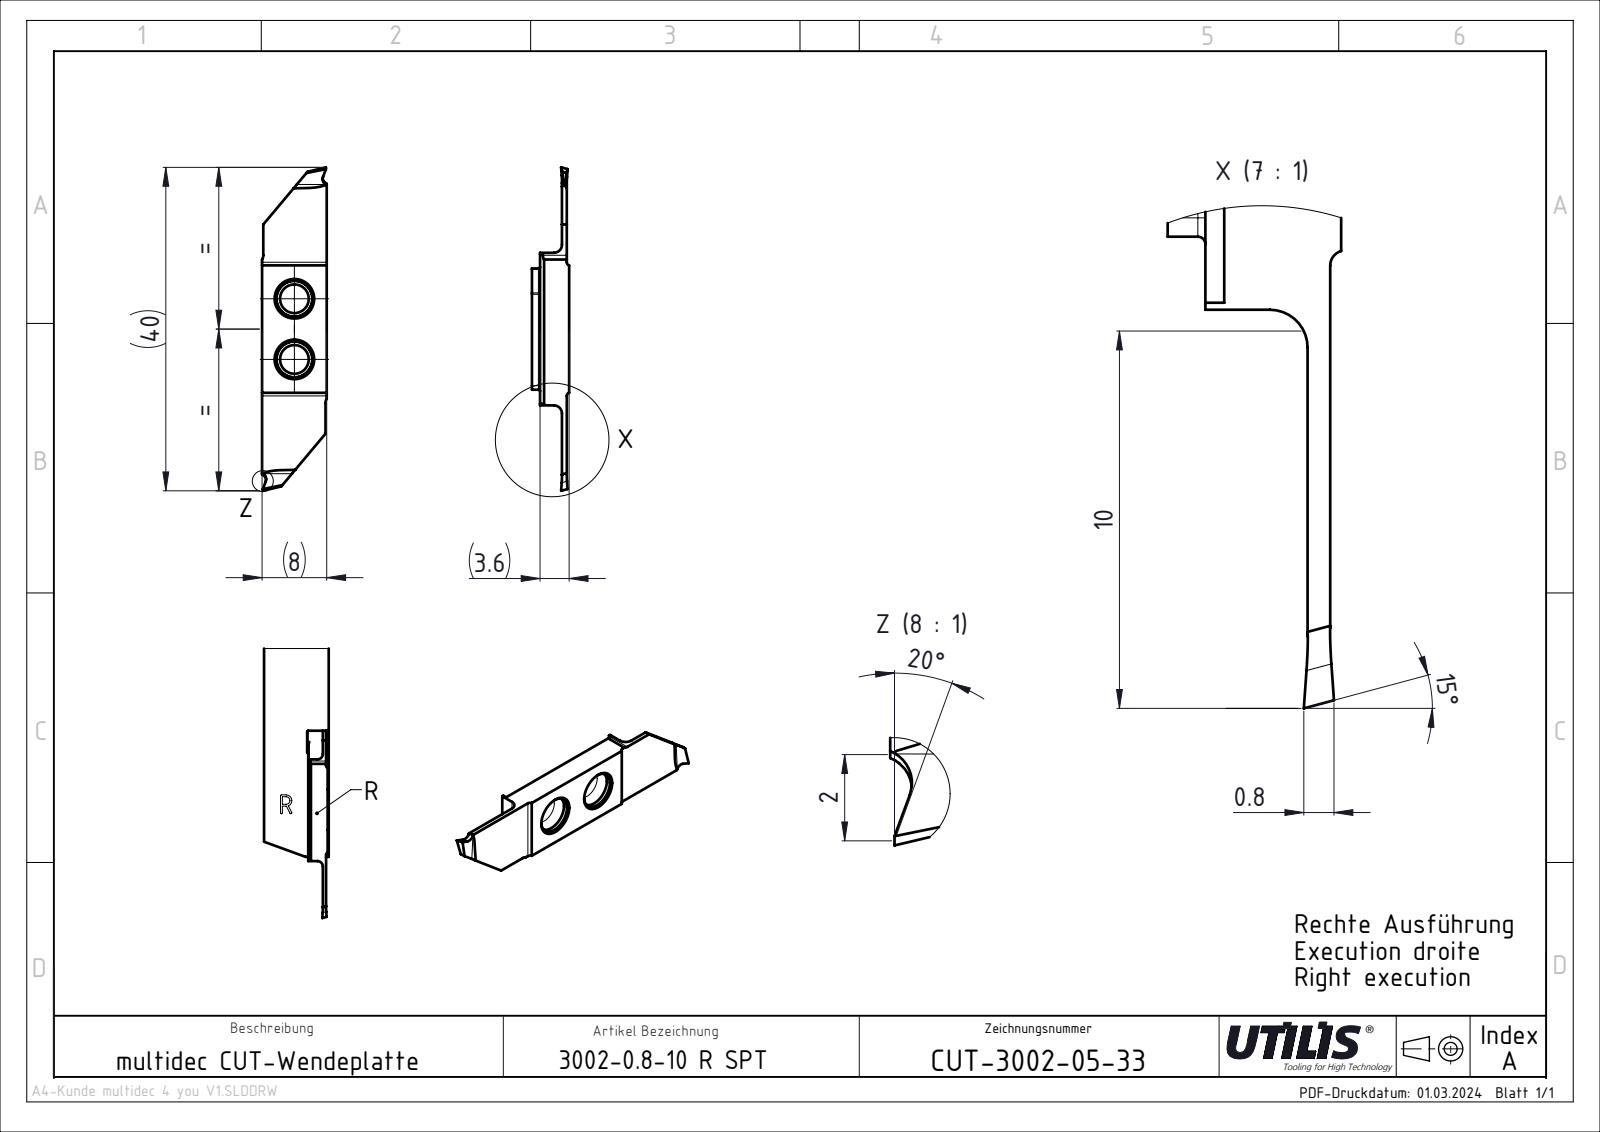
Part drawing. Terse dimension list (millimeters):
name: CUT-3002 SPT Slim_and_Deep; ASME Y14.5
written by: SolidWorks 2023 SP4 || FormatWorks Professional (AP242_MANAGED_MODEL_BASED_3D_ENGINEERING_MIM_LF)
unit: mm
bodies: 1 solid, 36 faces (26 planar, 10 cylindrical, 0 other)
size: 40 × 8 × 3.6
volume: 541 mm³; area: 785 mm²
holes: 2× ⌀3.55
rounds: 4× R1, 2× R0.4
face distances: 3.31, 3.6, 2.71, 0.6, 0.89, 8, 18.88, 1.27, 7.85, 22.54
hole spacings: 7.5
